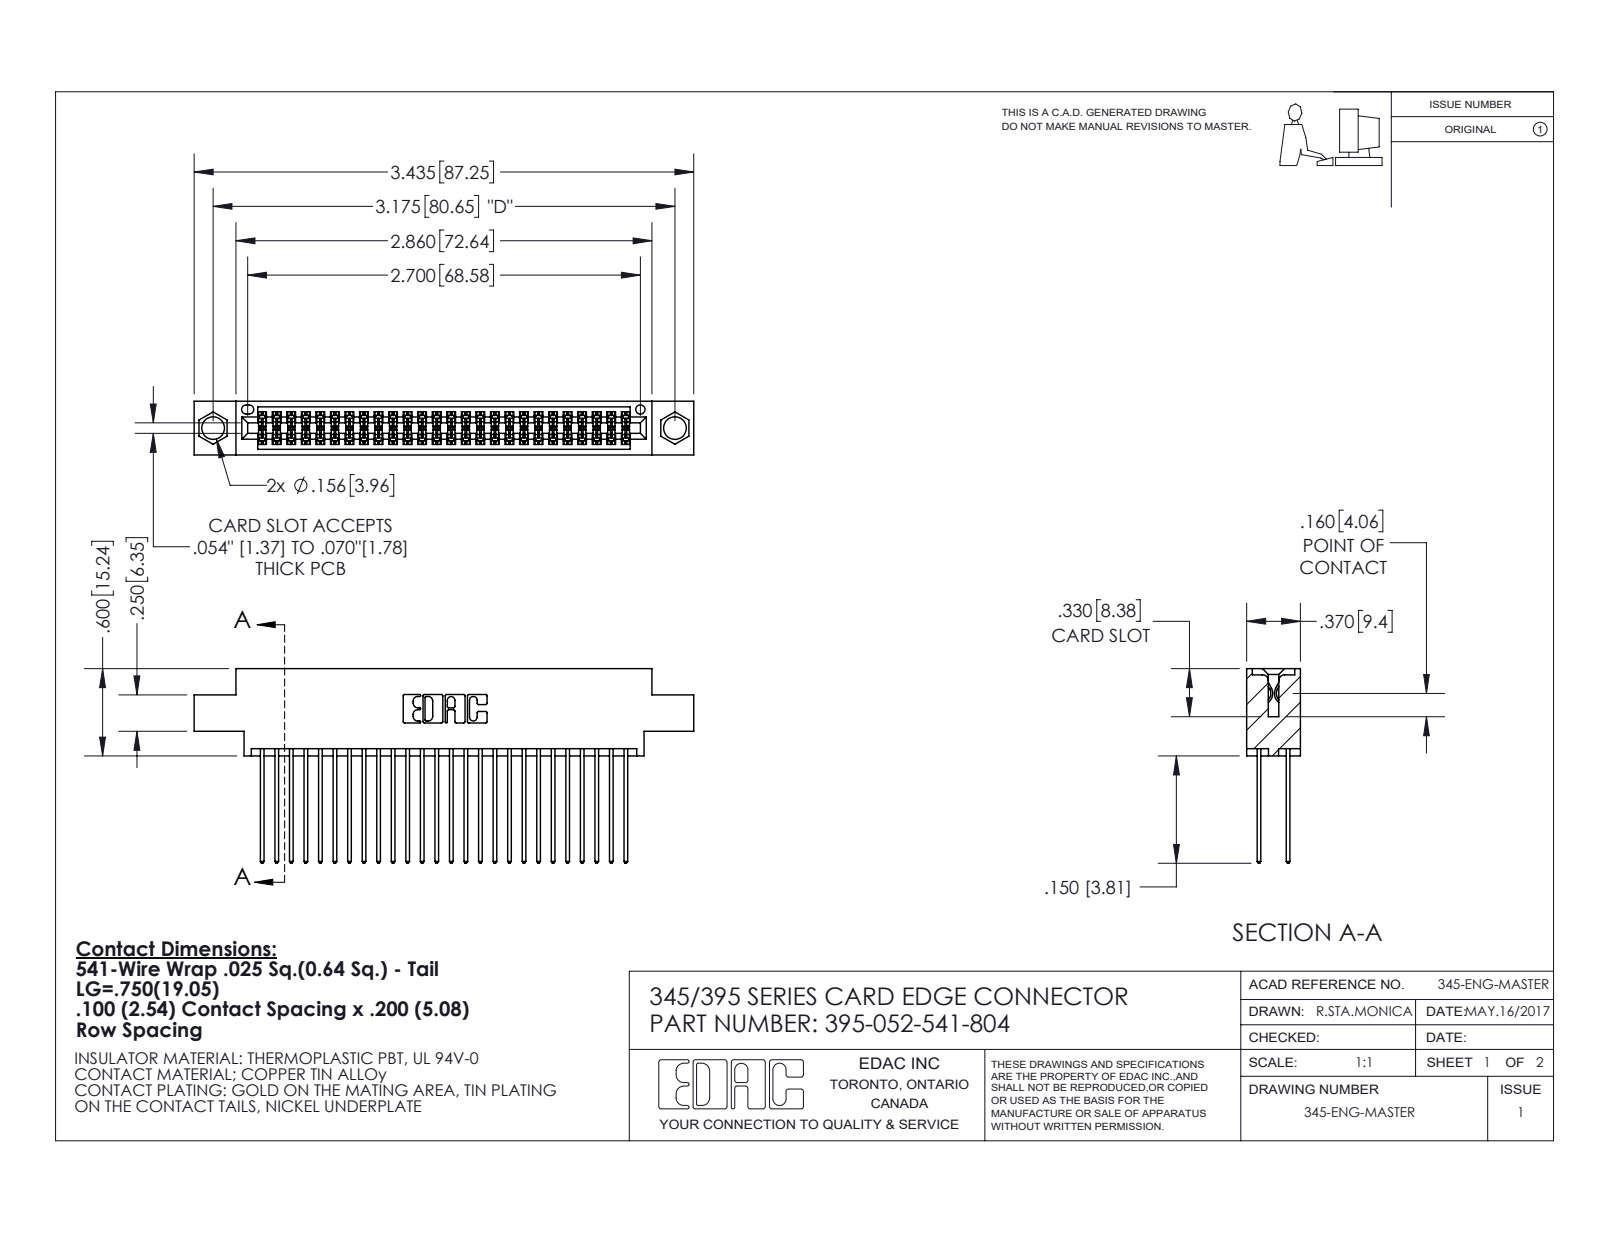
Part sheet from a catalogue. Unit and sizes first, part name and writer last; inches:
Units: inches
Overall size (bounding box): 3.435 × 1.337 × 0.37
Round holes (diameter × count): ⌀0.156 ×2, ⌀0.064 ×1
Partial cylindrical surfaces — rounded edges, fillets, slot ends (radius × count): R0.006 ×104, R0.01 ×52, R0.01 ×22, R0.007 ×6, R0.031 ×6, R0.026 ×3, R0.014 ×2, R0.019 ×2
Main face-to-face distances: 0.072, 0.298, 0.2, 0.098, 0.272, 0.025, 0.37, 0.225, 0.175, 0.149
Hole centre spacings: 0.27, 2.94, 3.175
Volume: 0.513 in³ · Surface area: 20.95 in²
Bodies: 53 solids, 2744 faces (1814 planar, 930 cylindrical, 0 other)
Part name (STEP PRODUCT): 345-292-001_345-293-141; 395-052-541-804; 345 Part_0.170 Offset - 0.156 Dia-TI
STEP written by: SolidWorks 2020 (CONFIG_CONTROL_DESIGN)
